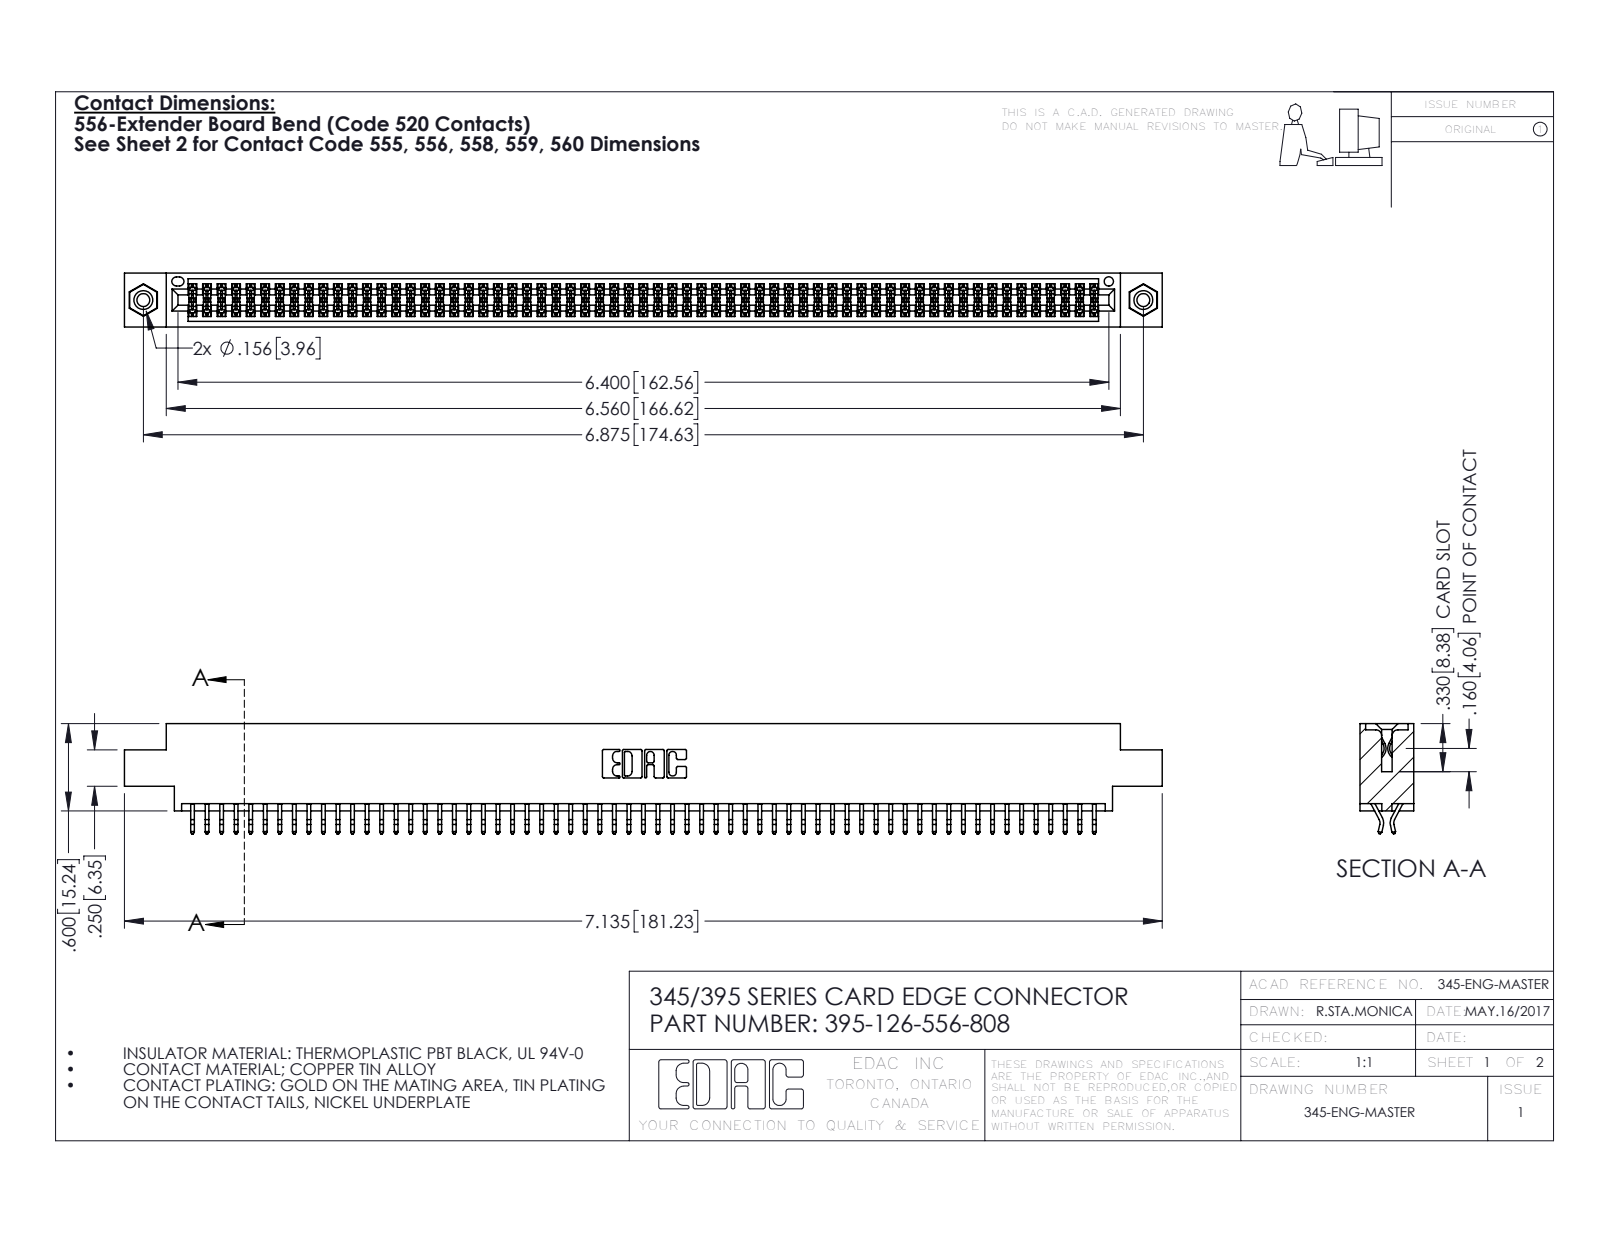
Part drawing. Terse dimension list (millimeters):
name: 345-250-001_345-250-003-102; 395-126-556-808; 345 Part_0.170 Offset - 0.156 Dia-TI; 345-292-001_556 Tail
written by: SolidWorks 2016 (CONFIG_CONTROL_DESIGN)
unit: mm
bodies: 129 solids, 7246 faces (4778 planar, 2452 cylindrical, 16 other)
size: 181.2 × 19.2 × 9.4
volume: 17 680 mm³; area: 26 580 mm²
holes: 2× ⌀2.3, 2× ⌀3.2, 2× ⌀4, 1× ⌀1.6
bosses: 2× ⌀3.9
rounds: 189× R0.2, 22× R0.3, 6× R0.2, 6× R0.8, 3× R0.7, 2× R0.3, 2× R0.4, 2× R0.5
face distances: 1.8, 7.6, 9.4, 5.1, 0.6, 2.5, 6.9, 5.7, 4.4, 3.8
hole spacings: 6.9, 168.6, 174.6
